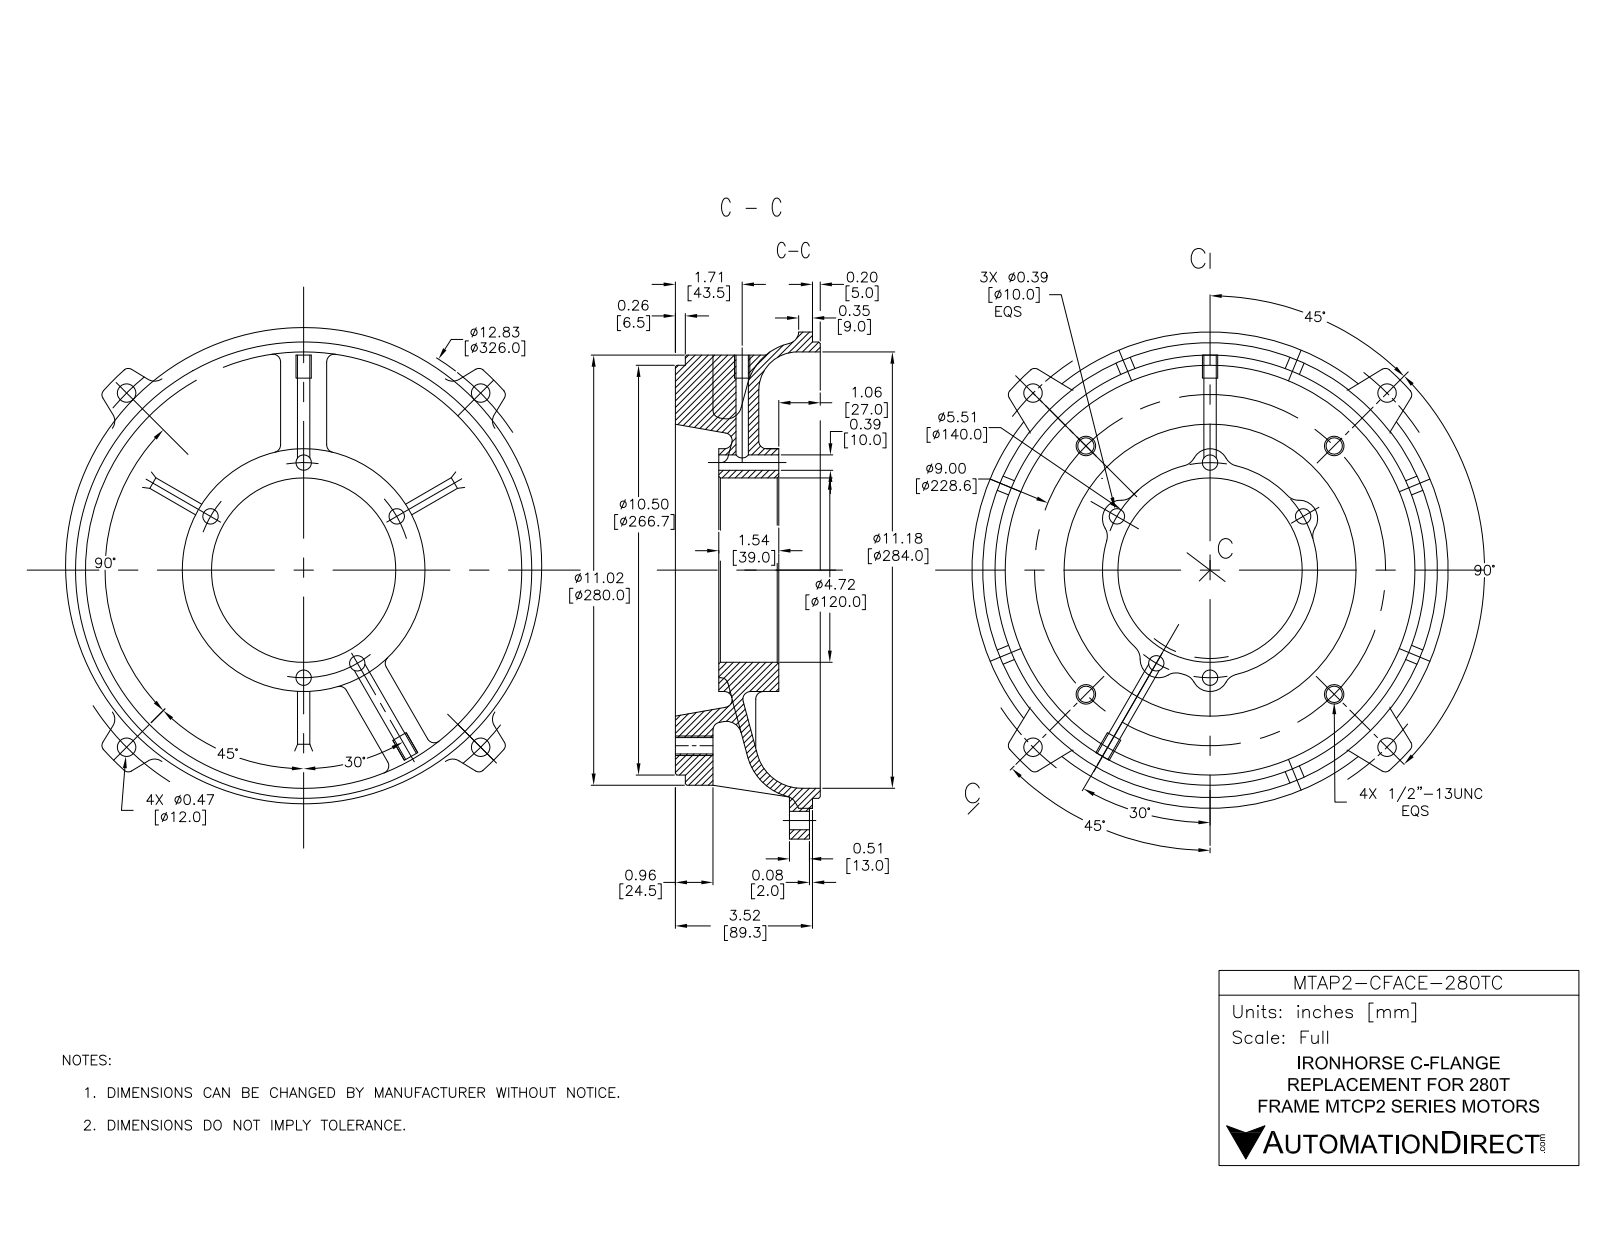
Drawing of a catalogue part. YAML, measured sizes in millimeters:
part_name: "MTAP2-CFACE-280TC"
step_written_by: "SolidWorks 2017 (AUTOMOTIVE_DESIGN)"
units: millimeters
bodies: {solids: 2, faces: 552, planar: 86, cylindrical: 175, other: 291}
overall_size: [310, 310, 94.3]
volume: 2047000
surface_area: 388700
round_holes:
  - {diameter: 12, count: 8}
  - {diameter: 10, count: 5}
  - {diameter: 8, count: 4}
  - {diameter: 22, count: 2}
  - {diameter: 55.5, count: 1}
  - {diameter: 78, count: 1}
  - {diameter: 110, count: 1}
  - {diameter: 284, count: 1}
round_bosses_or_shafts:
  - {diameter: 310, count: 1}
  - {diameter: 297, count: 1}
  - {diameter: 280, count: 1}
  - {diameter: 266.7, count: 1}
  - {diameter: 158, count: 1}
  - {diameter: 120, count: 1}
partial_cylinders:
  - {radius: 4, count: 22}
  - {radius: 5, count: 14}
  - {radius: 10, count: 10}
  - {radius: 8, count: 8}
  - {radius: 12, count: 5}
  - {radius: 45, count: 1}
  - {radius: 70, count: 1}
  - {radius: 175, count: 1}
face_to_face_distances: [24.5, 5, 28.3, 3.8, 22, 67.3, 42.8, 39, 66, 18]
hole_center_spacings: [199.1, 70, 48.7, 81.5, 83.8, 88, 114.3, 123.8]
